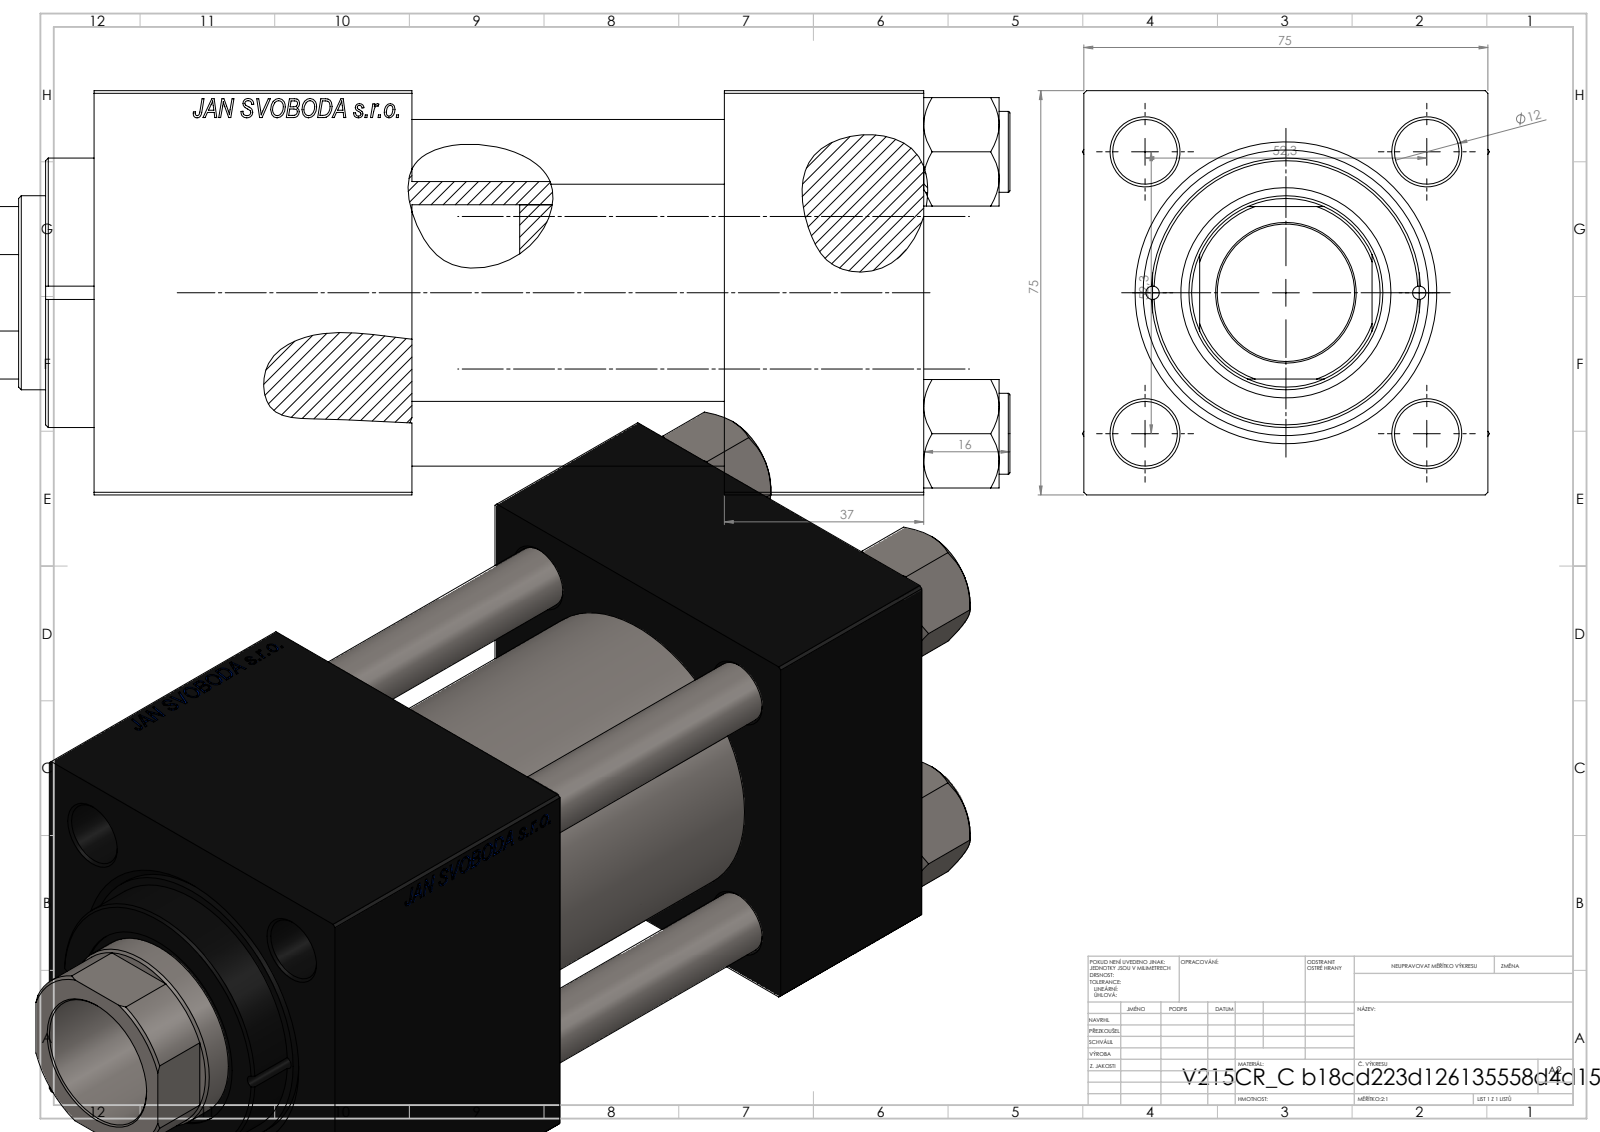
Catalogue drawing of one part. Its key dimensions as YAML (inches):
part_name: "V215_VC_A; V215CR_VCP_C; NUT_M5_C; V215CR_C_TYCINKA (+1 more)"
step_written_by: "SolidWorks 2019 (CONFIG_CONTROL_DESIGN)"
units: inches
bodies: {solids: 11, faces: 1155, planar: 528, cylindrical: 91, other: 536}
overall_size: [7.677, 2.974, 2.953]
volume: 41.85
surface_area: 241.2
round_holes:
  - {diameter: 0.472, count: 4}
  - {diameter: 0.098, count: 2}
  - {diameter: 0.276, count: 2}
  - {diameter: 0.825, count: 2}
  - {diameter: 1.181, count: 2}
  - {diameter: 1.004, count: 1}
  - {diameter: 1.417, count: 1}
  - {diameter: 1.535, count: 1}
  - {diameter: 1.614, count: 1}
  - {diameter: 2.087, count: 1}
round_bosses_or_shafts:
  - {diameter: 0.591, count: 4}
  - {diameter: 2.205, count: 1}
  - {diameter: 1.969, count: 1}
partial_cylinders:
  - {radius: 0.689, count: 1}
face_to_face_distances: [2.953, 1.457, 3.74, 2.283, 6.063, 4.606, 2.323, 4.933, 3.476, 1.193]
hole_center_spacings: [1.031, 1.456, 2.059, 2.253, 0.974, 2.912, 1.949, 3.681]
